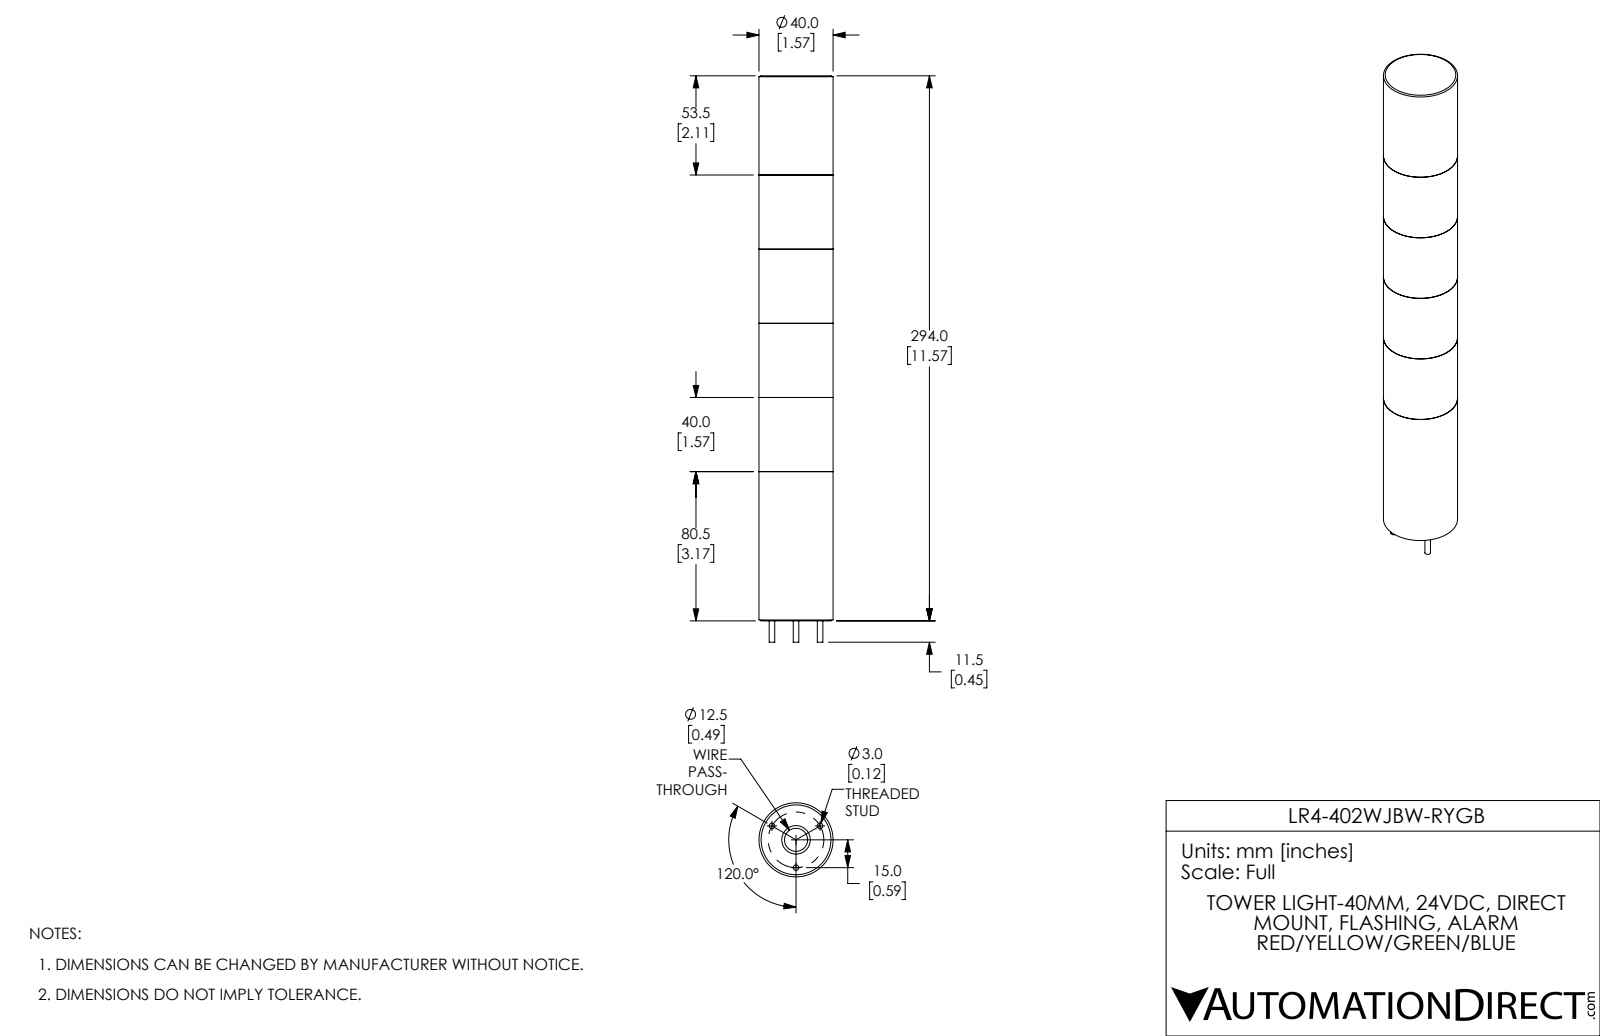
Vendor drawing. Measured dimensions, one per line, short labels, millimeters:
name: LR4-402WJBW-RYGB
written by: SolidWorks 2017 (AUTOMOTIVE_DESIGN)
unit: mm
bodies: 6 solids, 101 faces (37 planar, 62 cylindrical, 2 other)
size: 305.5 × 40 × 40
volume: 367 400 mm³; area: 64 160 mm²
holes: 1× ⌀12.5, 1× ⌀15.4, 1× ⌀35.2, 1× ⌀37.2, 1× ⌀37.5
bosses: 3× ⌀3, 1× ⌀40, 1× ⌀37.7, 1× ⌀37.1, 1× ⌀34.7
face distances: 40, 80, 120, 83.2, 43.2, 10.3, 123.2, 160, 50.3, 90.3
